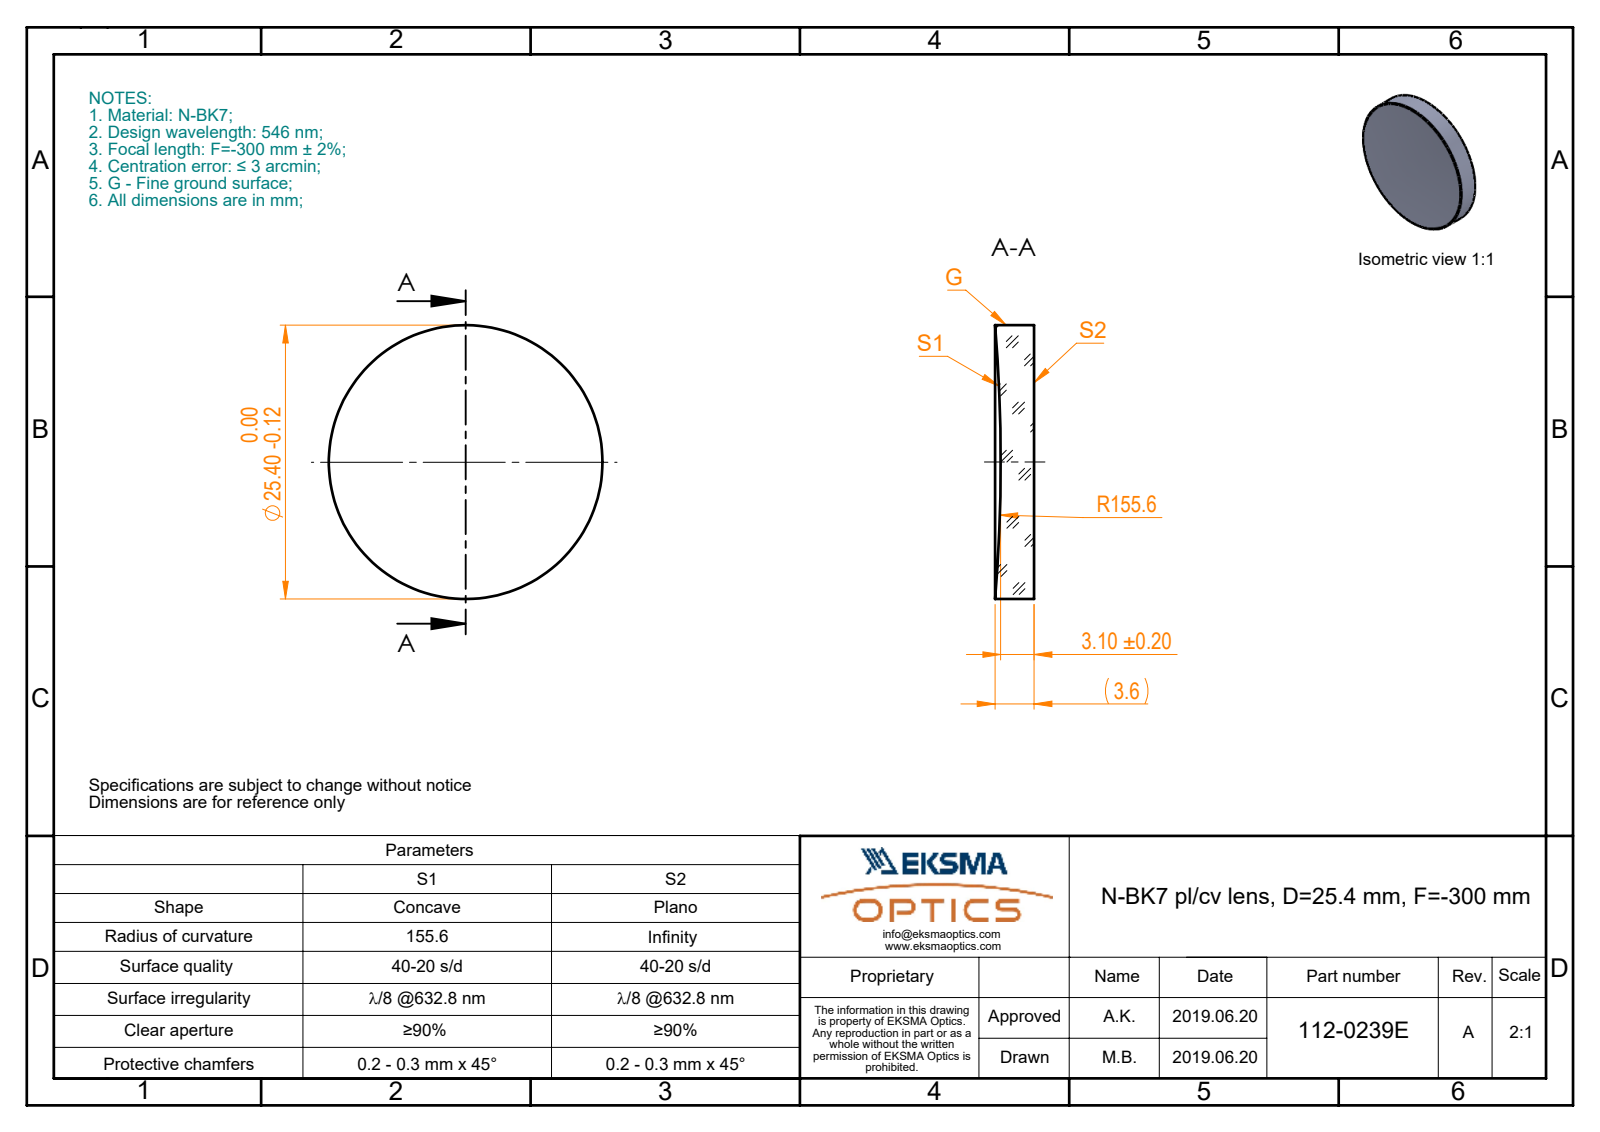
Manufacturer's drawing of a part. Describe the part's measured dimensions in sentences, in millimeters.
The part is named "112-0239E BK7 pl-cv 25.4 F-300". Its 3-D file was written by "SolidWorks 2017 (CONFIG_CONTROL_DESIGN)". It is 1 solid with 5 faces: 1 planar, 2 cylindrical and 2 other. Overall it measures 25.4 by 25.4 by 3.62 millimeters. Its volume is 1 702 cubic millimeters and its surface area 1 303 square millimeters. Round bosses or shafts: 1 of diameter 25.4.
